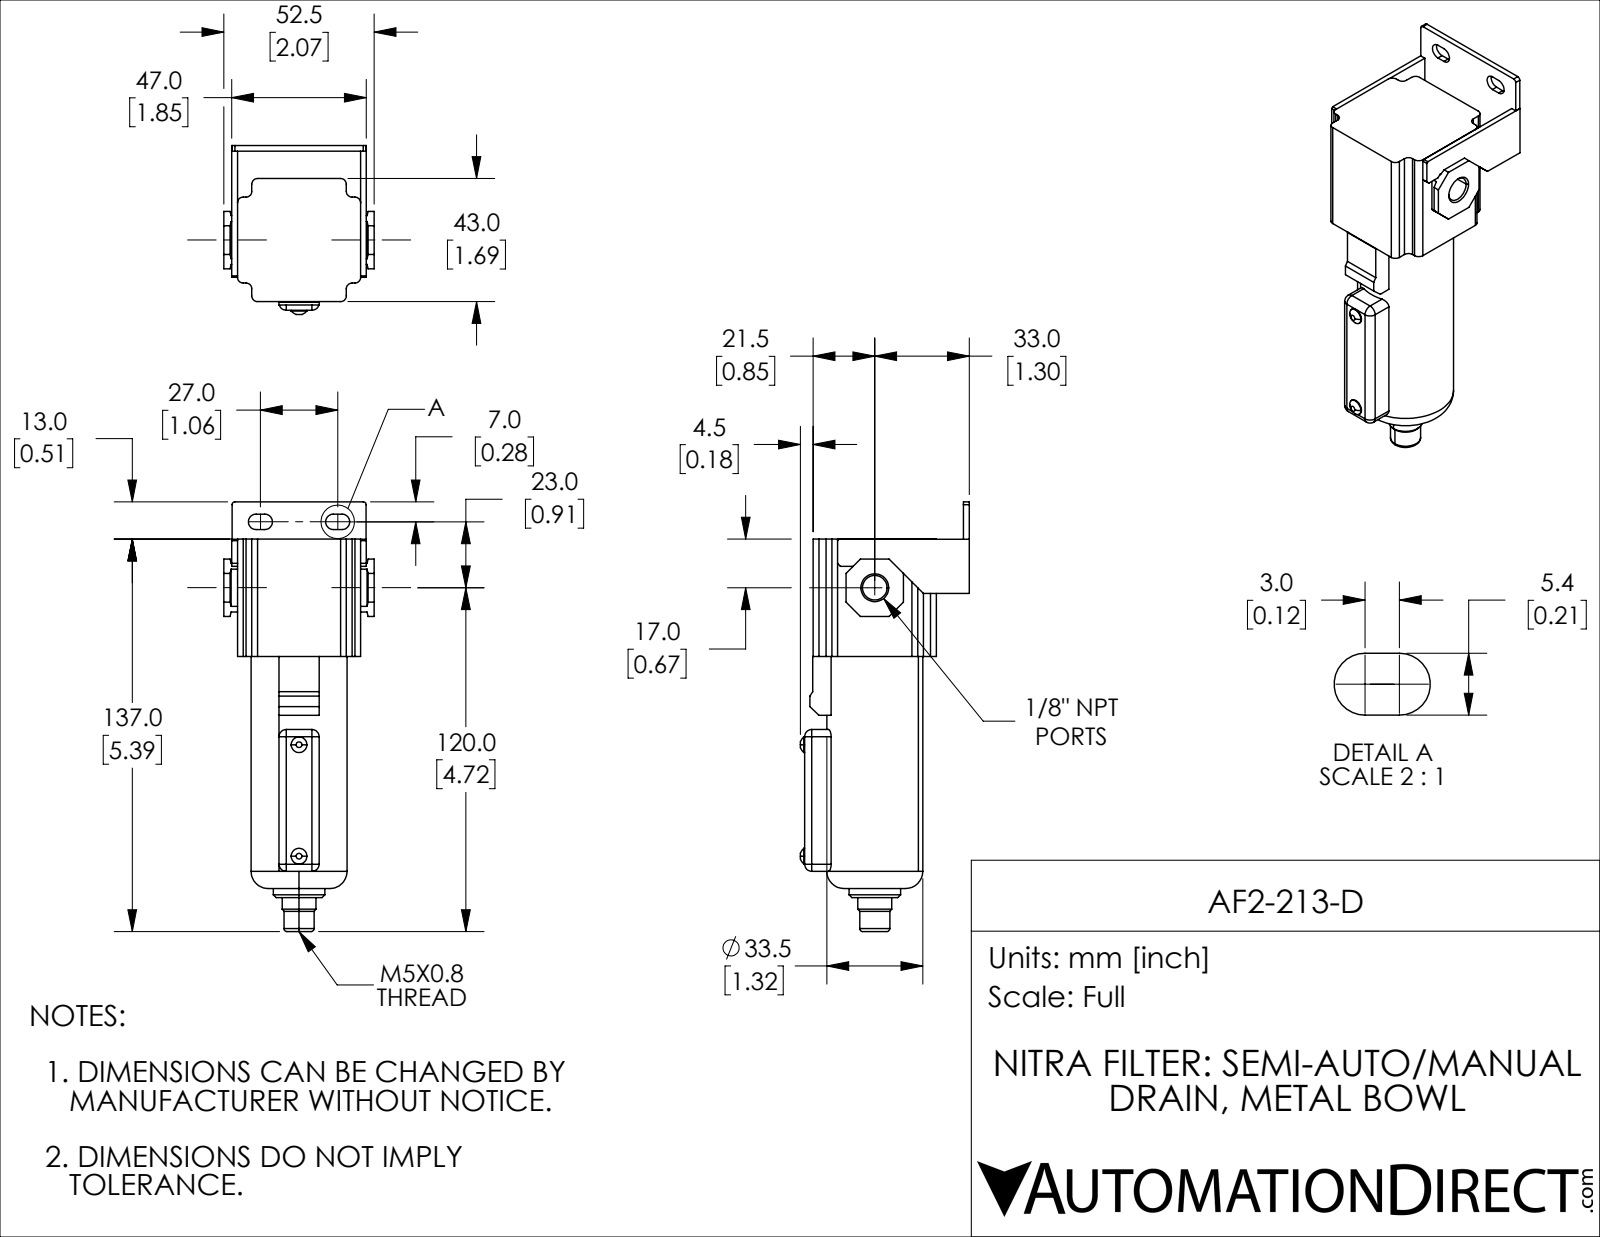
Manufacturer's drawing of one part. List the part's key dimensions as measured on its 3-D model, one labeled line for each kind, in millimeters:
Part name (STEP PRODUCT): AF2-213-D
STEP written by: SolidWorks 2019 (CONFIG_CONTROL_DESIGN)
Units: millimetres
Bodies: 1 solid, 164 faces (97 planar, 45 cylindrical, 22 other)
Overall size (bounding box): 150 × 59 × 52.5
Volume: 156 956 mm³ · Surface area: 26 291 mm²
Round holes (diameter × count): ⌀4.13 ×1, ⌀8.57 ×1
Round bosses / shafts (diameter × count): ⌀5.5 ×2, ⌀33.5 ×1, ⌀18 ×1, ⌀11.8 ×1, ⌀10.5 ×1
Partial cylindrical surfaces — rounded edges, fillets, slot ends (radius × count): R2 ×12, R2.5 ×8, R2.7 ×4, R1 ×2
Main face-to-face distances: 2, 43, 9.5, 52.5, 11.5, 54.5, 45, 14.5, 16.5, 30.5
